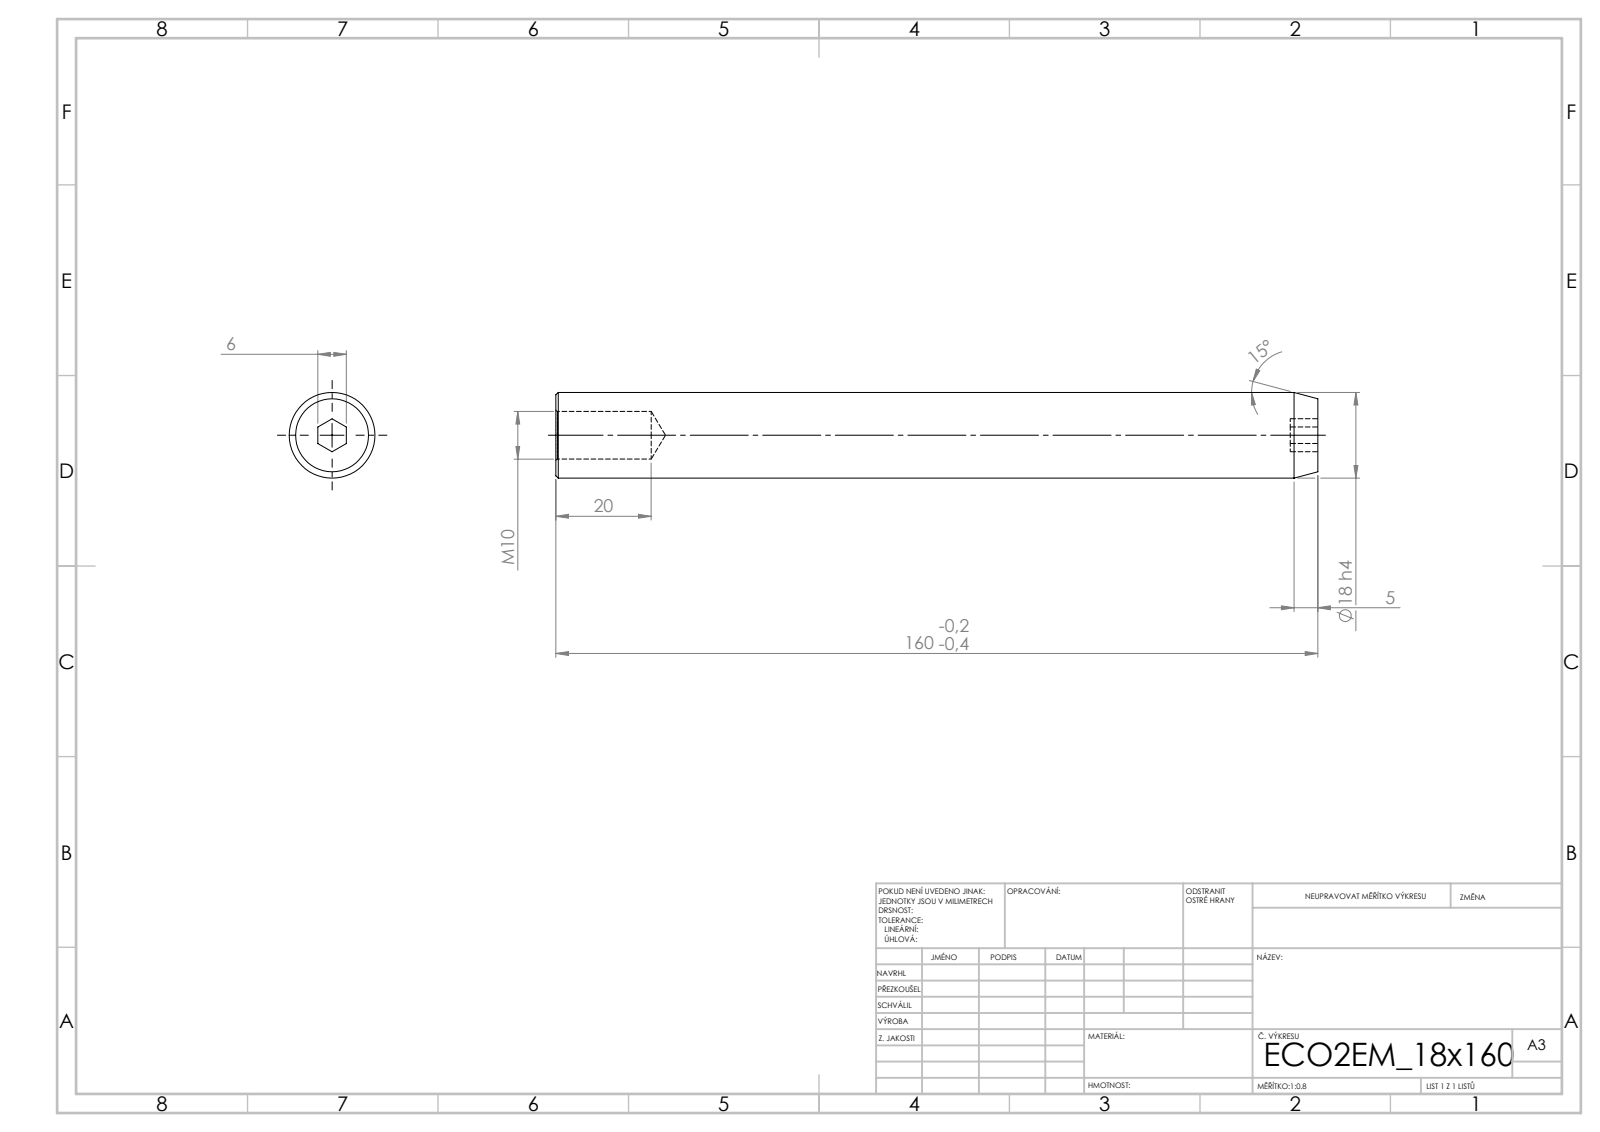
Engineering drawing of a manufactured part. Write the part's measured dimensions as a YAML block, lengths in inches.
step_written_by: "SolidWorks 2019 (CONFIG_CONTROL_DESIGN)"
units: inches
bodies: {solids: 1, faces: 21, planar: 9, cylindrical: 4, other: 8}
overall_size: [6.299, 0.709, 0.709]
volume: 2.361
surface_area: 15.83
round_holes:
  - {diameter: 0.394, count: 1}
round_bosses_or_shafts:
  - {diameter: 0.709, count: 1}
face_to_face_distances: [6.299, 0.236, 0.228, 6.071]
